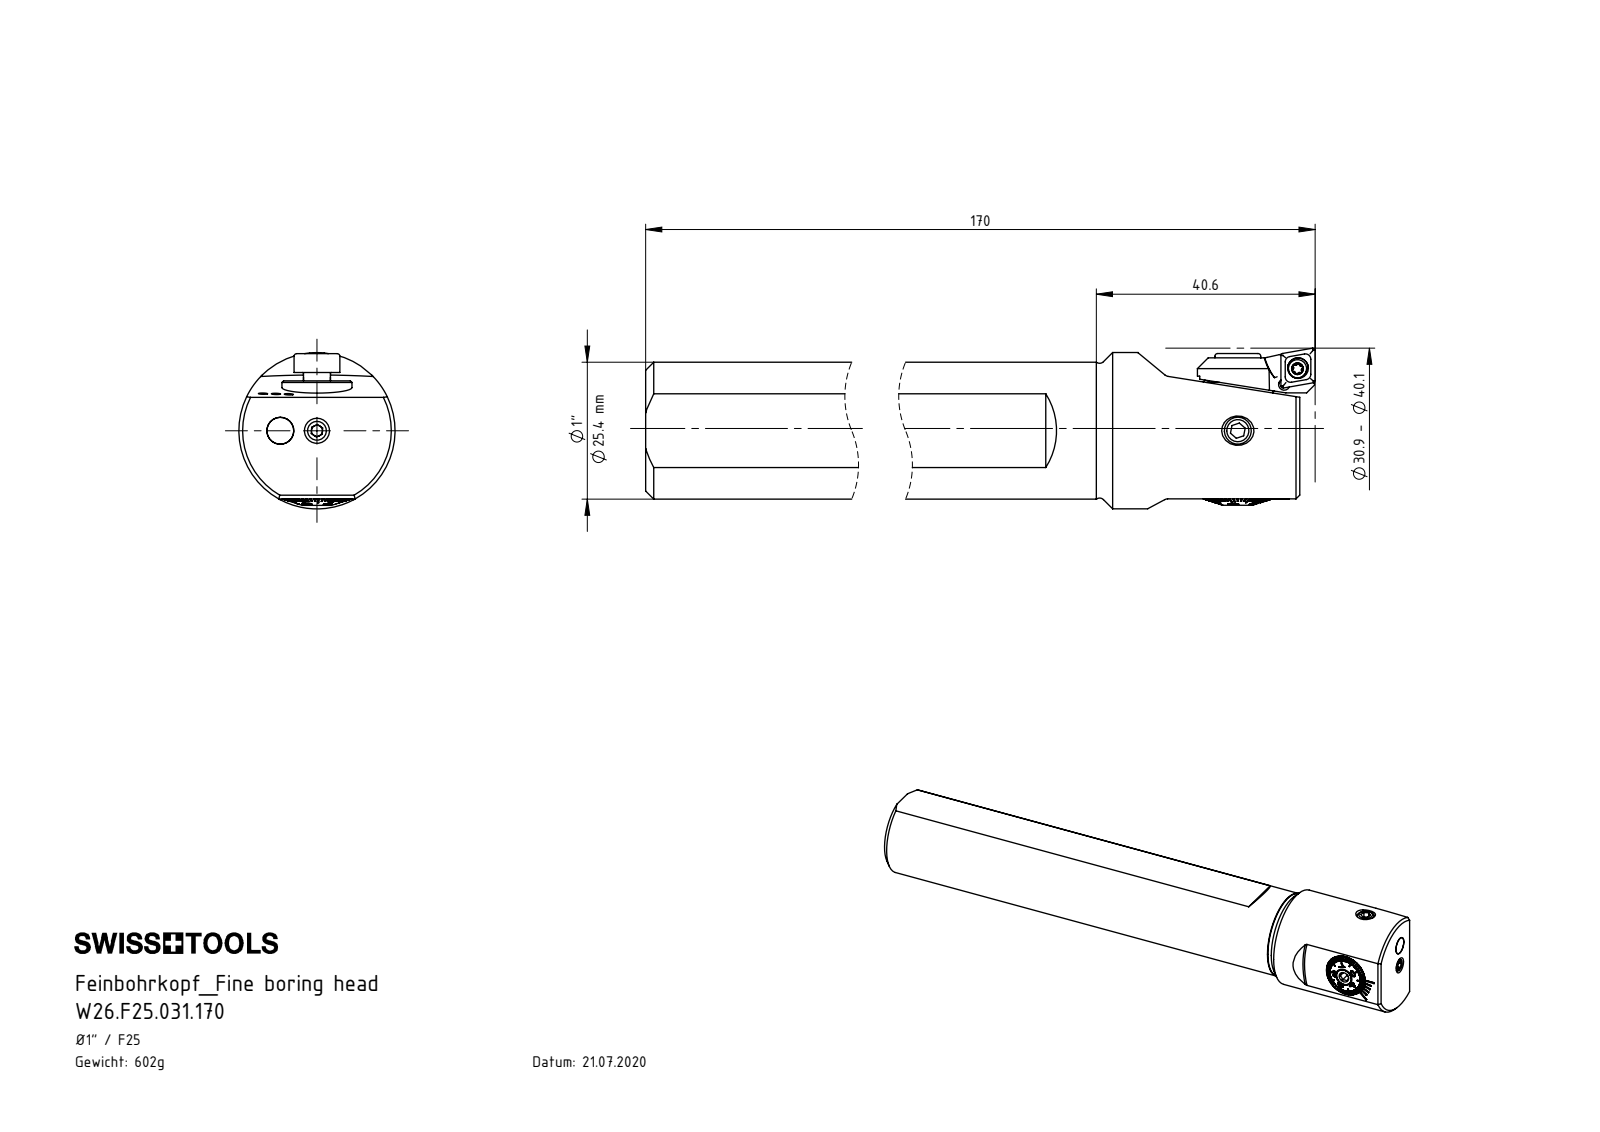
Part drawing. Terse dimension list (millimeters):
name: F25-BG2.010.011_A; DIN 7984 - M5 x 8; F25-BG1.DA3.013_A_Aktuell 06.2014-M1x2; F25-BG3.005.018_B (+8 more)
written by: SolidWorks 2017 (AUTOMOTIVE_DESIGN)
unit: mm
bodies: 13 solids, 526 faces (306 planar, 60 cylindrical, 160 other)
size: 167.15 × 29 × 29
volume: 76 194 mm³; area: 23 784 mm²
holes: 3× ⌀1.5, 2× ⌀2.5, 2× ⌀4.2, 1× ⌀2.05, 1× ⌀2.4, 1× ⌀2.7, 1× ⌀3, 1× ⌀3.3, 1× ⌀5, 1× ⌀5.5, 1× ⌀6.4, 1× ⌀7.3
bosses: 2× ⌀5, 2× ⌀4.95, 1× ⌀29, 1× ⌀25.4, 1× ⌀13, 1× ⌀12.98, 1× ⌀12.85, 1× ⌀10.65
rounds: 4× R1.4, 2× R0.5, 2× R1.5, 1× R0.2, 1× R1.25, 1× R2
face distances: 167.15, 1.5, 3.91, 3.1, 0.81, 1.6, 2.31, 18, 19.6, 21.1
hole spacings: 6.8, 7.32
